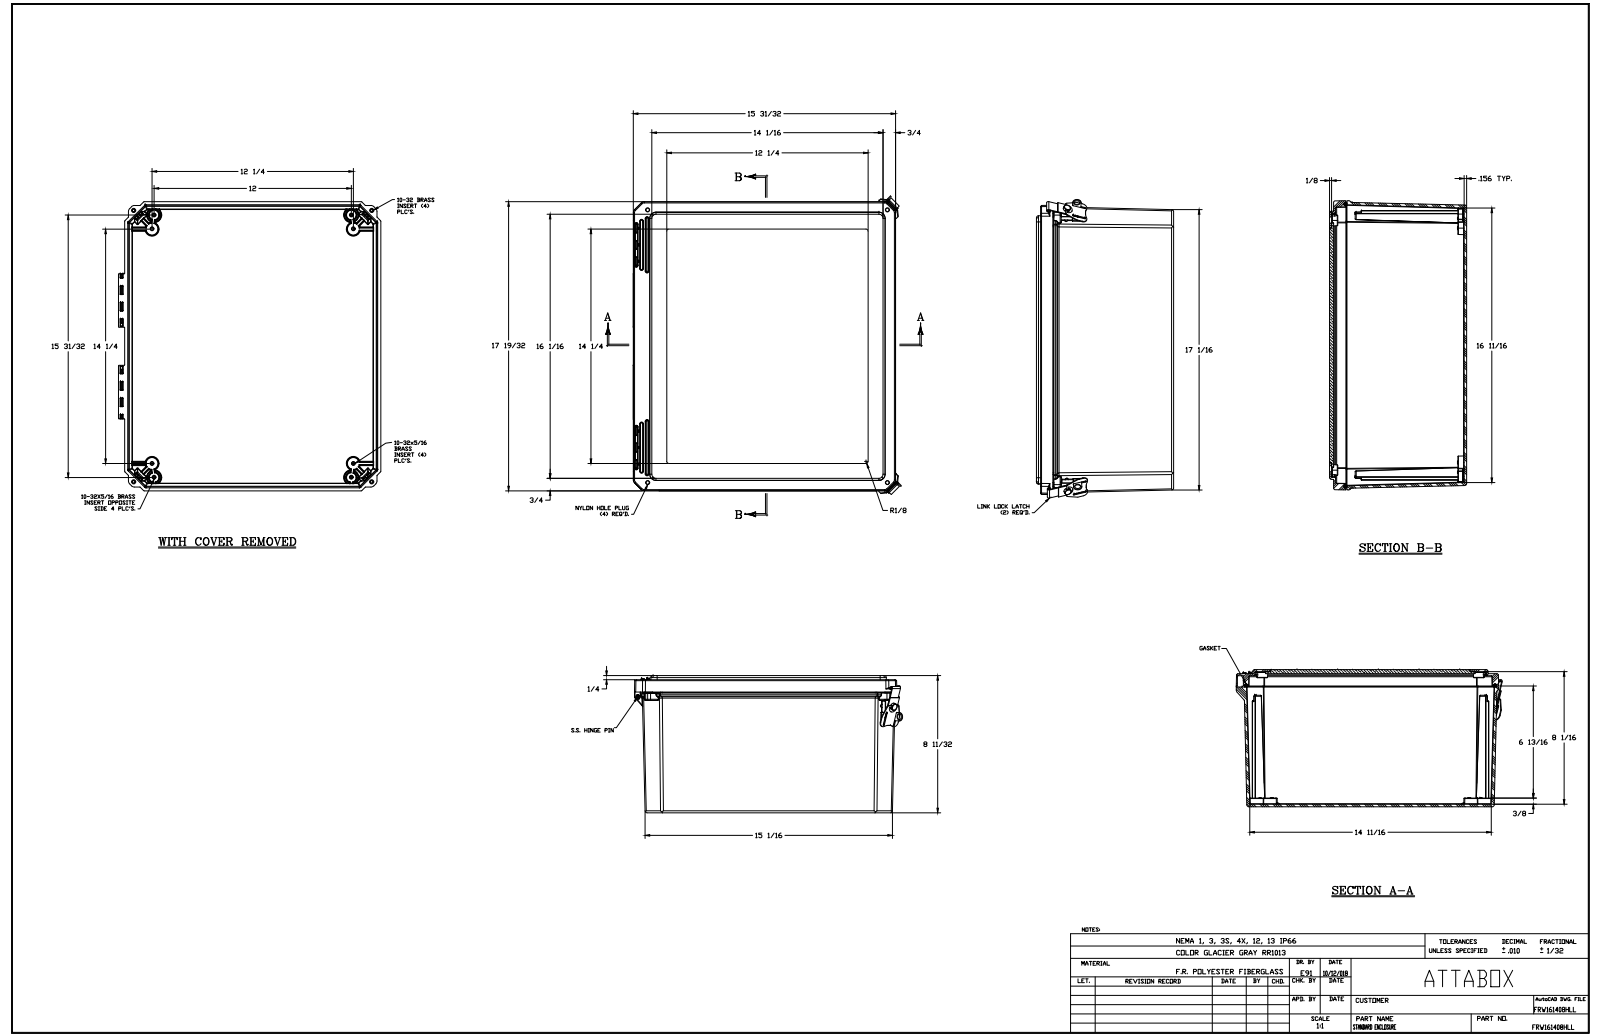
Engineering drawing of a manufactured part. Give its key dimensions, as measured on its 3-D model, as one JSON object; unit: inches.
{"part_name": "FRW161408HLL", "step_written_by": "SolidWorks 2018 (AUTOMOTIVE_DESIGN)", "units": "inches", "bodies": {"solids": 38, "faces": 2367, "planar": 826, "cylindrical": 932, "other": 609}, "overall_size": [18.47, 16.405, 8.343], "volume_in3": 203, "surface_area_in2": 2303, "round_holes": [[0.156, 16], [0.152, 8], [0.098, 4], [0.15, 4], [0.252, 4], [0.253, 4], [0.05, 2], [0.12, 2], [0.219, 2], [0.227, 2], [0.313, 2], [0.363, 2]], "round_bosses_or_shafts": [[0.246, 16], [0.209, 4], [0.2, 4], [0.6, 2], [0.135, 2], [0.05, 2], [0.435, 1], [0.435, 1]], "partial_cylinders_radius": [[0.01, 195], [0.005, 80], [0.02, 57], [0.03, 45], [0.125, 38], [0.039, 28], [0.03, 24], [0.09, 24]], "face_to_face_distances": [0.156, 0.18, 0.181, 8.119, 7.963, 8.343, 8.187, 0.225, 0.125, 0.25], "hole_center_spacings": [20.438, 0.865, 1.651, 12.155, 13.469, 15.106, 15.461, 1.33]}
